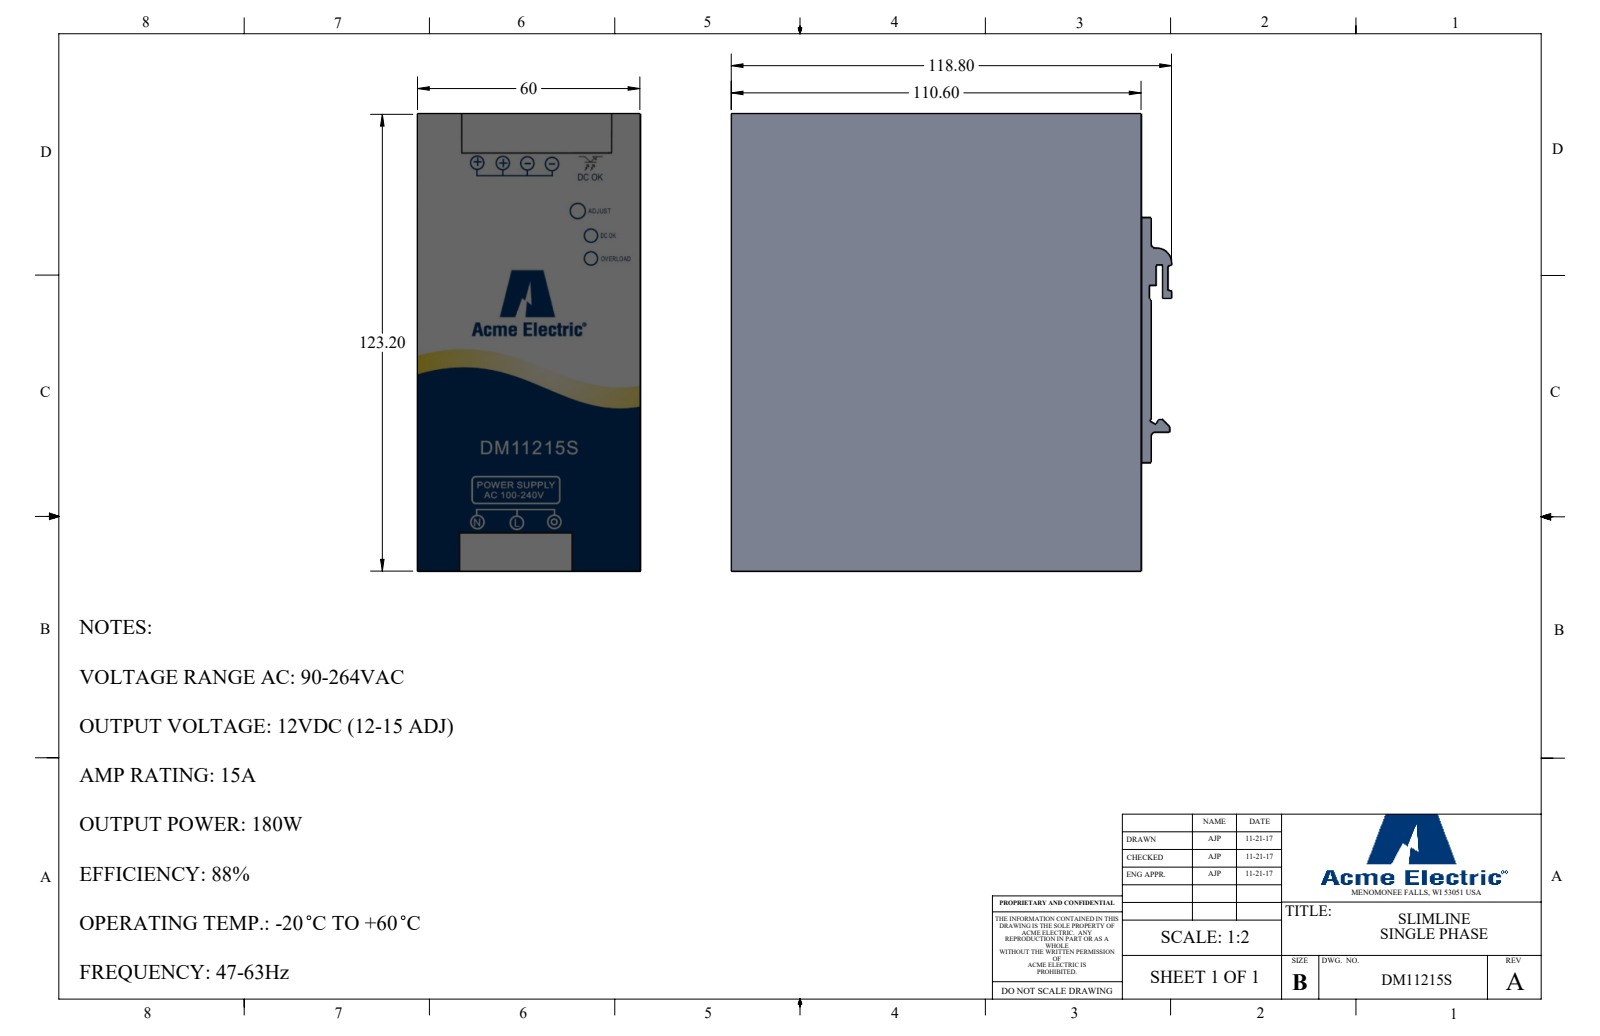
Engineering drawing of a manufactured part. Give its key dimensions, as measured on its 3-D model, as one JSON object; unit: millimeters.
{"part_name": "DM11215S", "step_written_by": "SolidWorks 2017 (AUTOMOTIVE_DESIGN)", "units": "millimeters", "bodies": {"solids": 1, "faces": 36, "planar": 33, "cylindrical": 3, "other": 0}, "overall_size": [123.2, 118.8, 60], "volume_mm3": 828374, "surface_area_mm2": 57842, "partial_cylinders_radius": [[1, 2], [4, 1]], "face_to_face_distances": [60, 123.2, 110.6, 2.7, 113.3, 7, 53, 3, 5.7, 116.3]}
